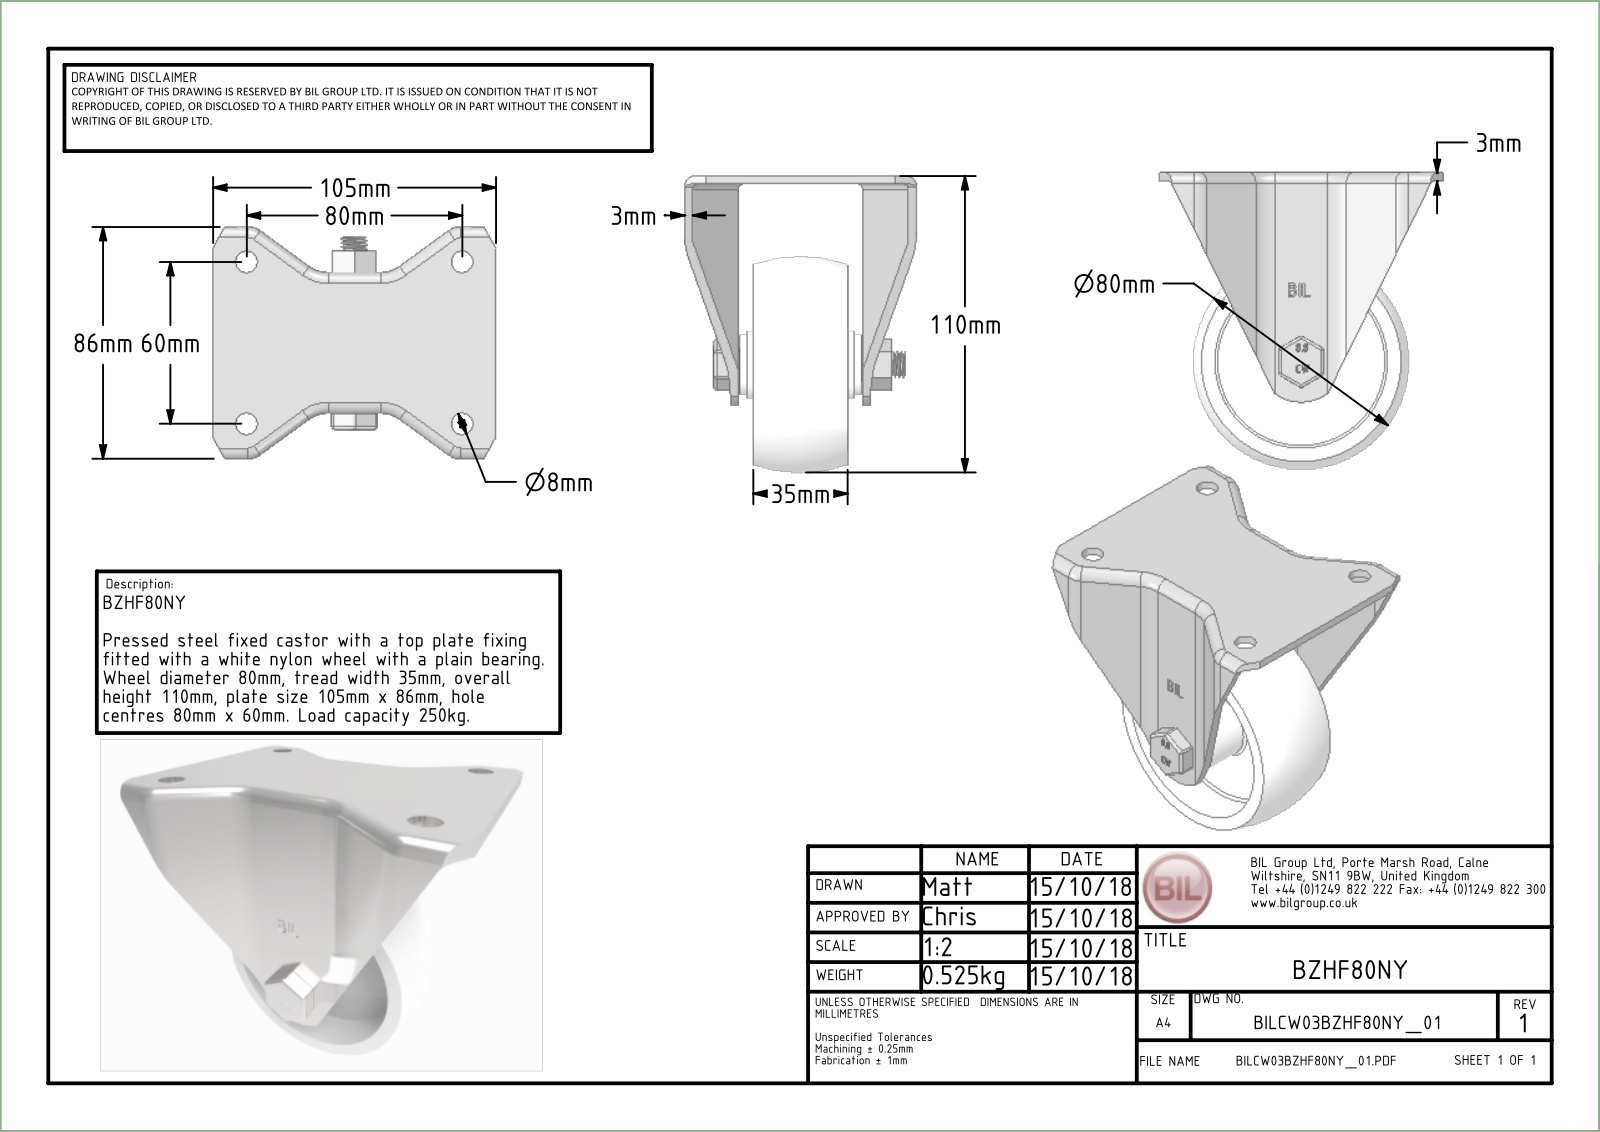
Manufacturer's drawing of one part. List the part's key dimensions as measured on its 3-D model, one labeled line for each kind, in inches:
Part name (STEP PRODUCT): BZHF80NY v4; BZHF80AS v1; BZHF80AS; ZINC PLATED, PRESSED STEEL BRACKET (+8 more)
STEP written by: Autodesk Translation Framework v14.4.0.0 (AUTOMOTIVE_DESIGN)
Units: inches
Bodies: 6 solids, 383 faces (148 planar, 133 cylindrical, 102 other)
Overall size (bounding box): 4.331 × 4.134 × 3.425
Volume: 8.875 in³ · Surface area: 109.9 in²
Round holes (diameter × count): ⌀0.394 ×1, ⌀0.402 ×1, ⌀0.472 ×1, ⌀0.492 ×1
Round bosses / shafts (diameter × count): ⌀0.984 ×1, ⌀0.886 ×1, ⌀0.63 ×1, ⌀0.47 ×1, ⌀0.388 ×1, ⌀0.32 ×1
Partial cylindrical surfaces — rounded edges, fillets, slot ends (radius × count): R0.02 ×18, R0.118 ×12, R0.059 ×10, R0.394 ×9, R0.177 ×8, R0.03 ×6, R0.276 ×4, R0.512 ×4
Main face-to-face distances: 0.118, 1.004, 0.197, 0.079, 2.008, 1.201, 2.087, 0.886, 1.083, 1.791
